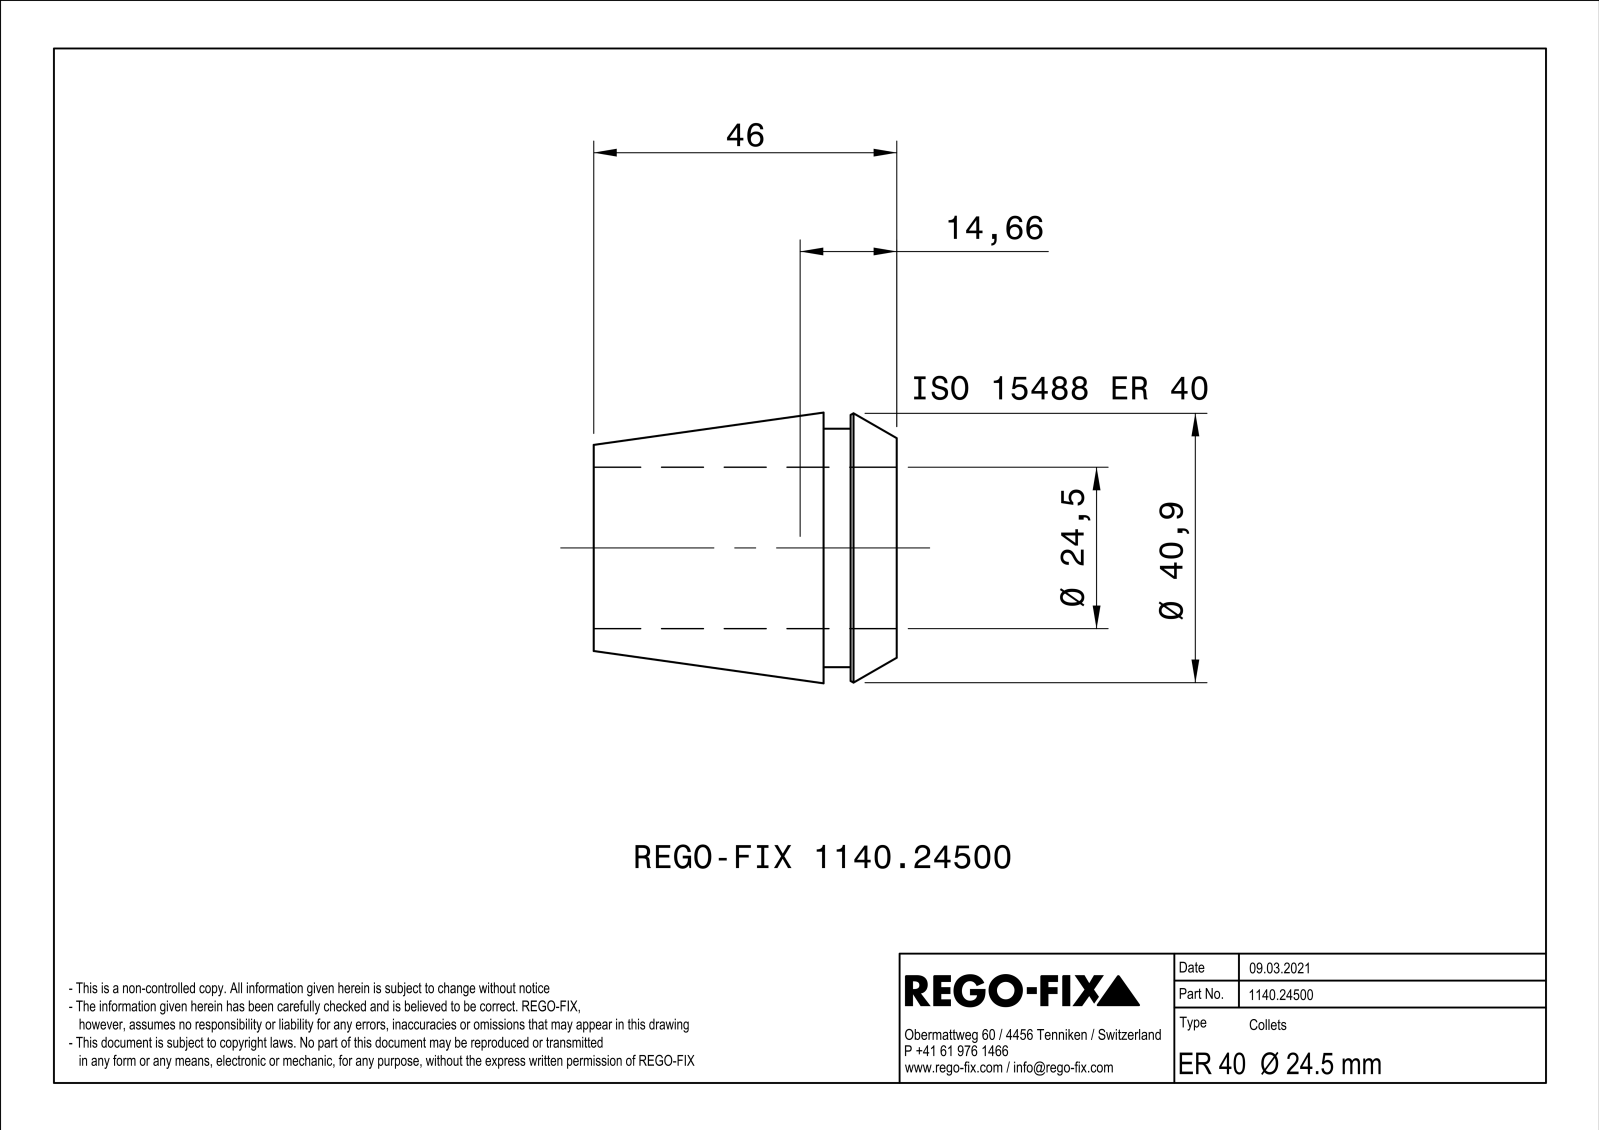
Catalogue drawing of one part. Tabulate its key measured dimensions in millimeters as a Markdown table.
| quantity | value |
| --- | --- |
| part name | NOCUT |
| STEP written by | SIEMENS PLM Software Solid Edge ST10 (AUTOMOTIVE_DESIGN) |
| units | millimeters |
| bodies | 1 solid, 177 faces (88 planar, 9 cylindrical, 80 other) |
| overall size | 46 × 40.99 × 40.99 |
| volume | 22 290 mm³ |
| surface area | 16 495 mm² |
| round holes (diameter × count) | 24.5 × 1 |
| round bosses / shafts (diameter × count) | 36.2 × 1 |
| main face-to-face distances | 1, 11.1, 7, 4.1, 46, 39, 34.9, 7.5, 0.5, 3.6 |
